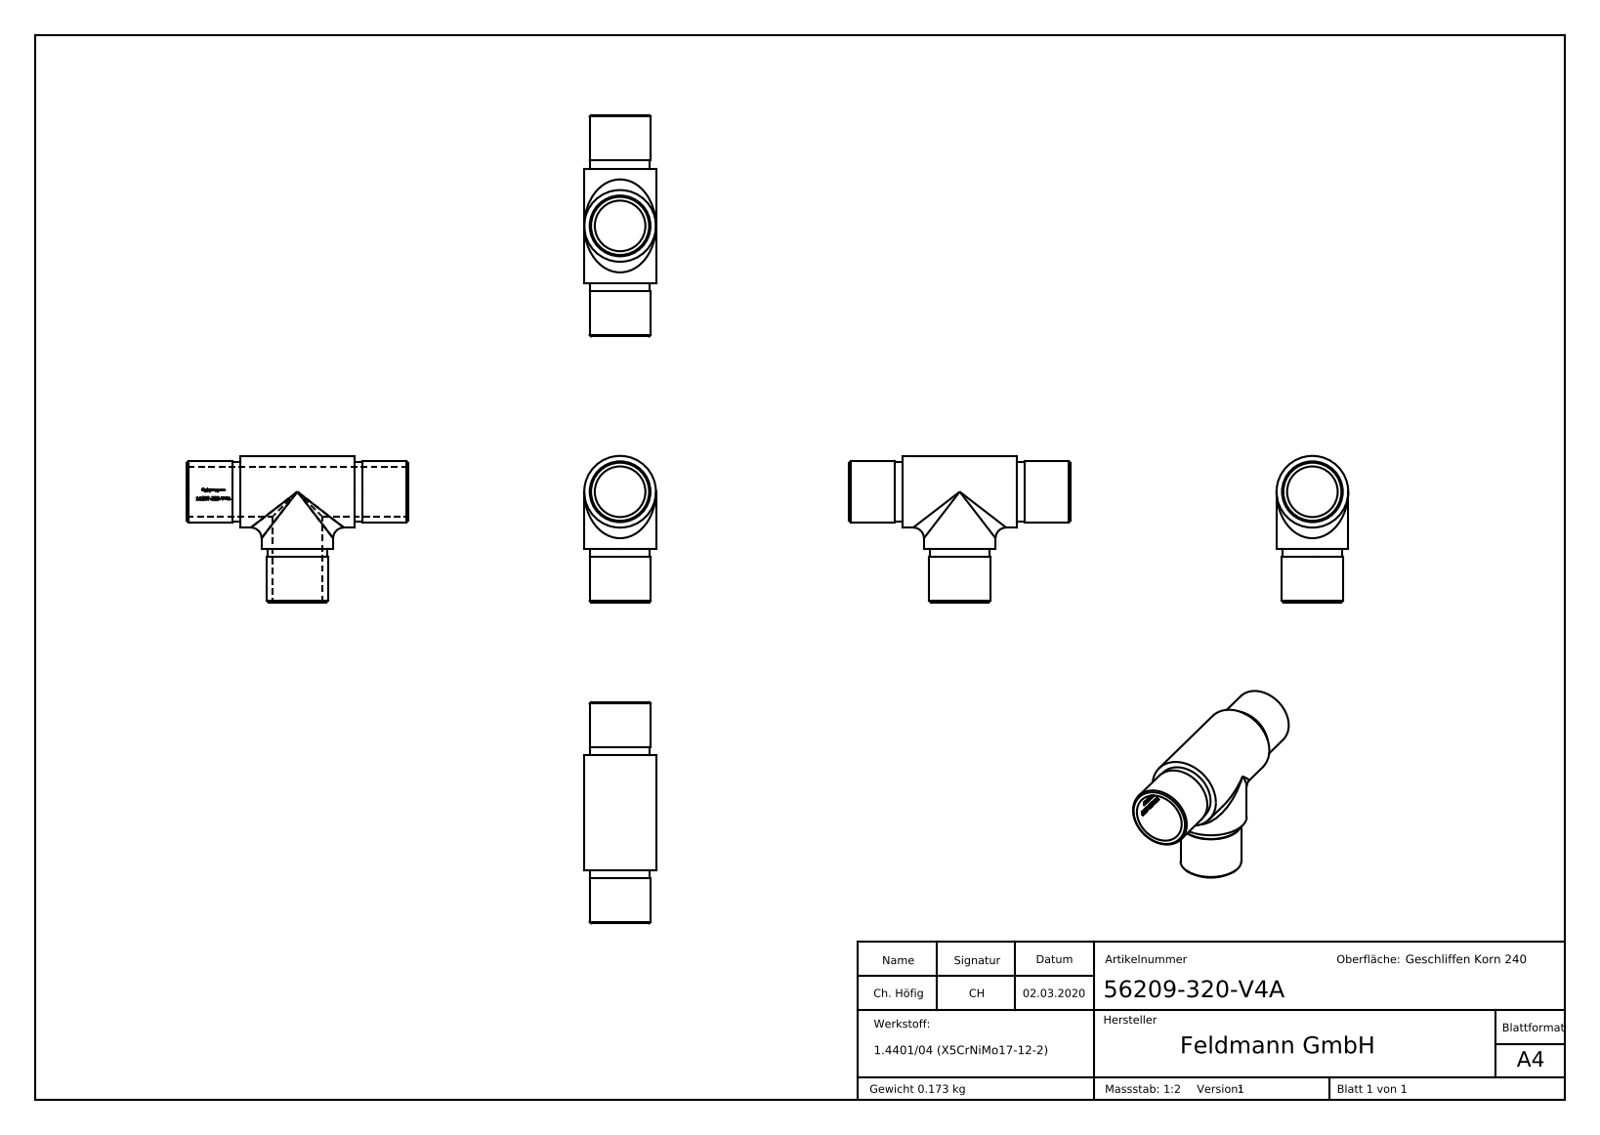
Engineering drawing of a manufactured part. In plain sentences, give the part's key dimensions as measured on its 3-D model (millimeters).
The part is named "56209-320-V4A". Its 3-D file was written by "SolidWorks 2015 (CONFIG_CONTROL_DESIGN)". It is 1 solid with 292 faces: 129 planar, 40 cylindrical and 123 other. Overall it measures 83 by 54.95 by 26.9 millimeters. Its volume is 21 612 cubic millimeters and its surface area 15 839 square millimeters. Round holes: 2 of diameter 19. Round bosses or shafts: 2 of diameter 26.9, 2 of diameter 22.8, 2 of diameter 22.4. Partial cylindrical surfaces (rounded edges, fillets, slot ends): 1 of radius 9.6. The main face-to-face distances are 20, 63, 43, 83, 17, 3, 66, 46, 49, 3.36.
